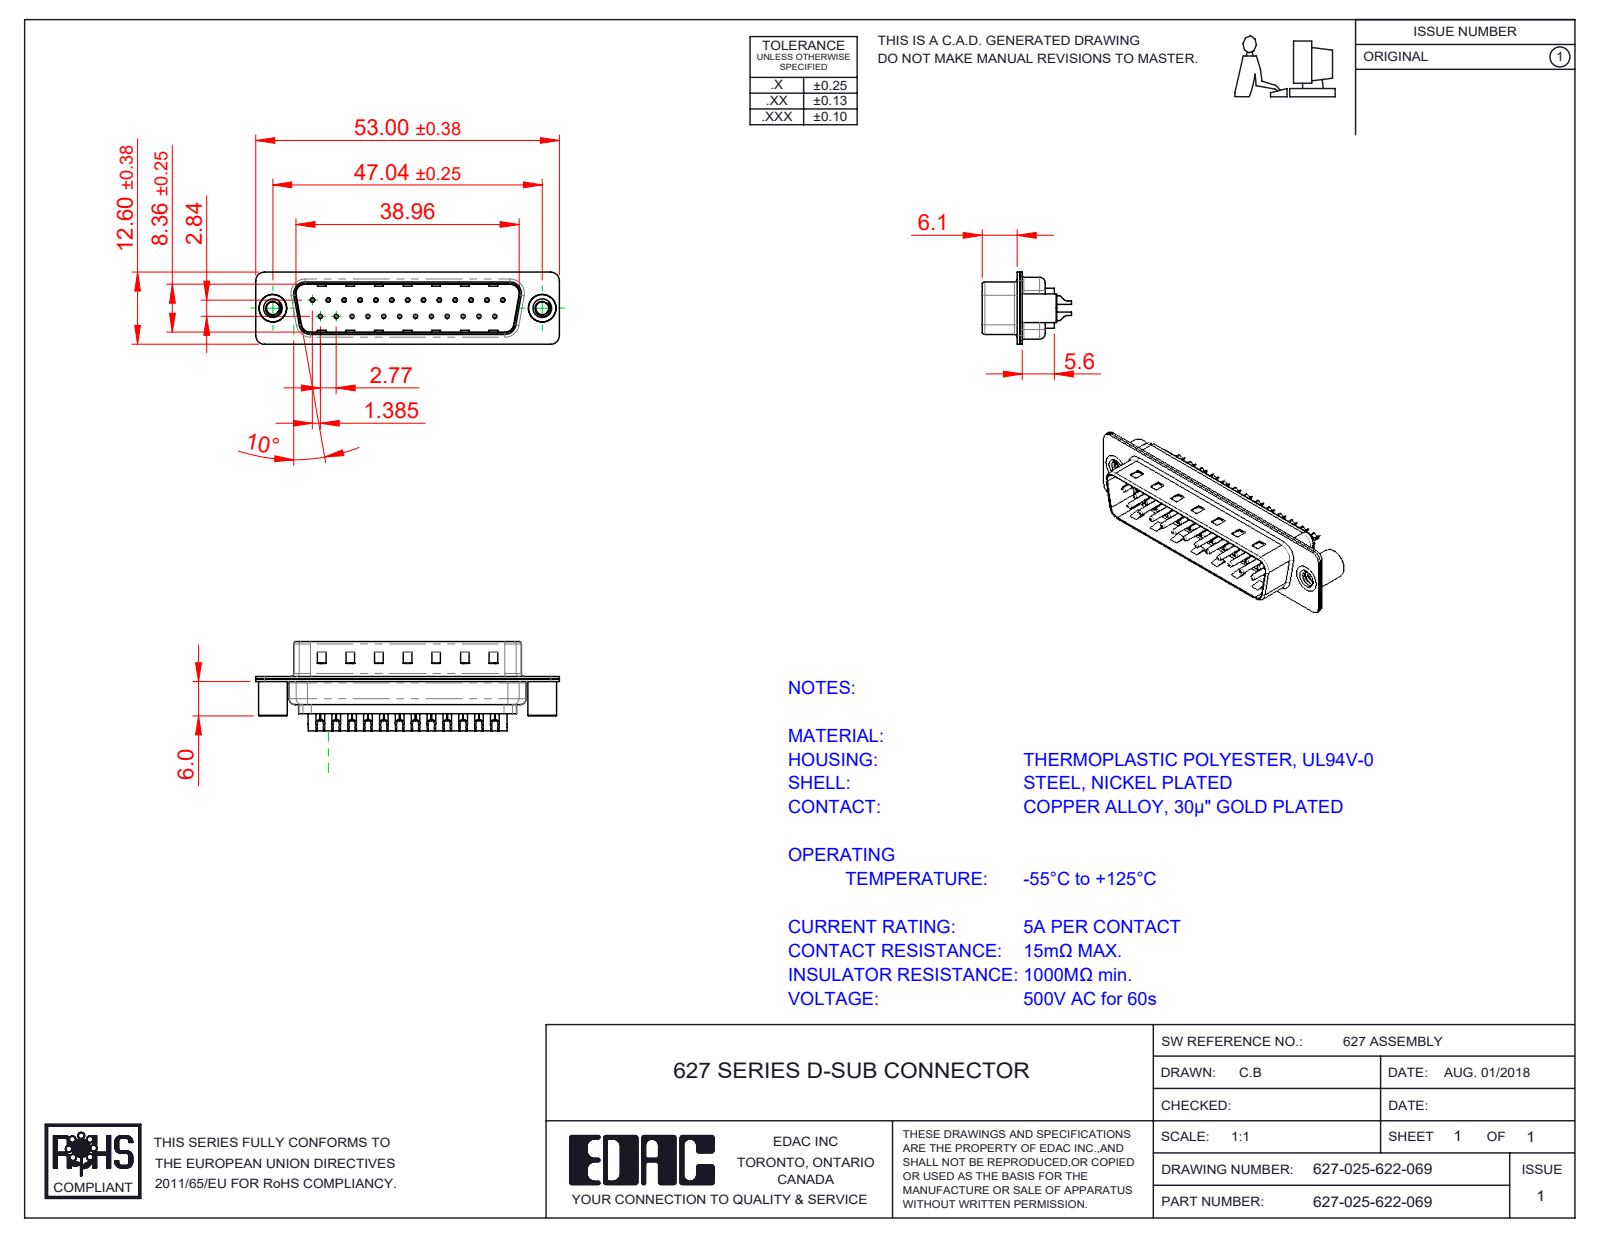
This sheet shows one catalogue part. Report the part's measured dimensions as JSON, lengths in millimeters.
{"part_name": "627 Shell Front_25 Contacts; 627 Housing_25 LP; 627-025-622-069; 627 Shell Rear_25 Contacts (+3 more)", "step_written_by": "SolidWorks 2020 (CONFIG_CONTROL_DESIGN)", "units": "millimeters", "bodies": {"solids": 30, "faces": 1998, "planar": 521, "cylindrical": 882, "other": 595}, "overall_size": [53, 15.35, 12.6], "volume_mm3": 2787, "surface_area_mm2": 8046, "round_holes": [[0.35, 25], [1.1, 25], [1.6, 25], [2.26, 2], [4, 2], [4.8, 2]], "round_bosses_or_shafts": [[2, 25], [1.5, 25], [0.75, 25], [5, 2], [4.9, 2]], "partial_cylinders_radius": [[1.5, 16], [2, 12], [0.5, 8], [1.6, 8], [1, 6], [0.25, 4], [0.6, 4], [0.65, 4]], "face_to_face_distances": [0.4, 0.45, 0.82, 9.58, 8.76, 0.9, 1.5, 6.5, 1.4, 6.05], "hole_center_spacings": [3.16, 8.31, 2.77, 5.54, 11.08, 16.62, 5.03, 5.04]}
